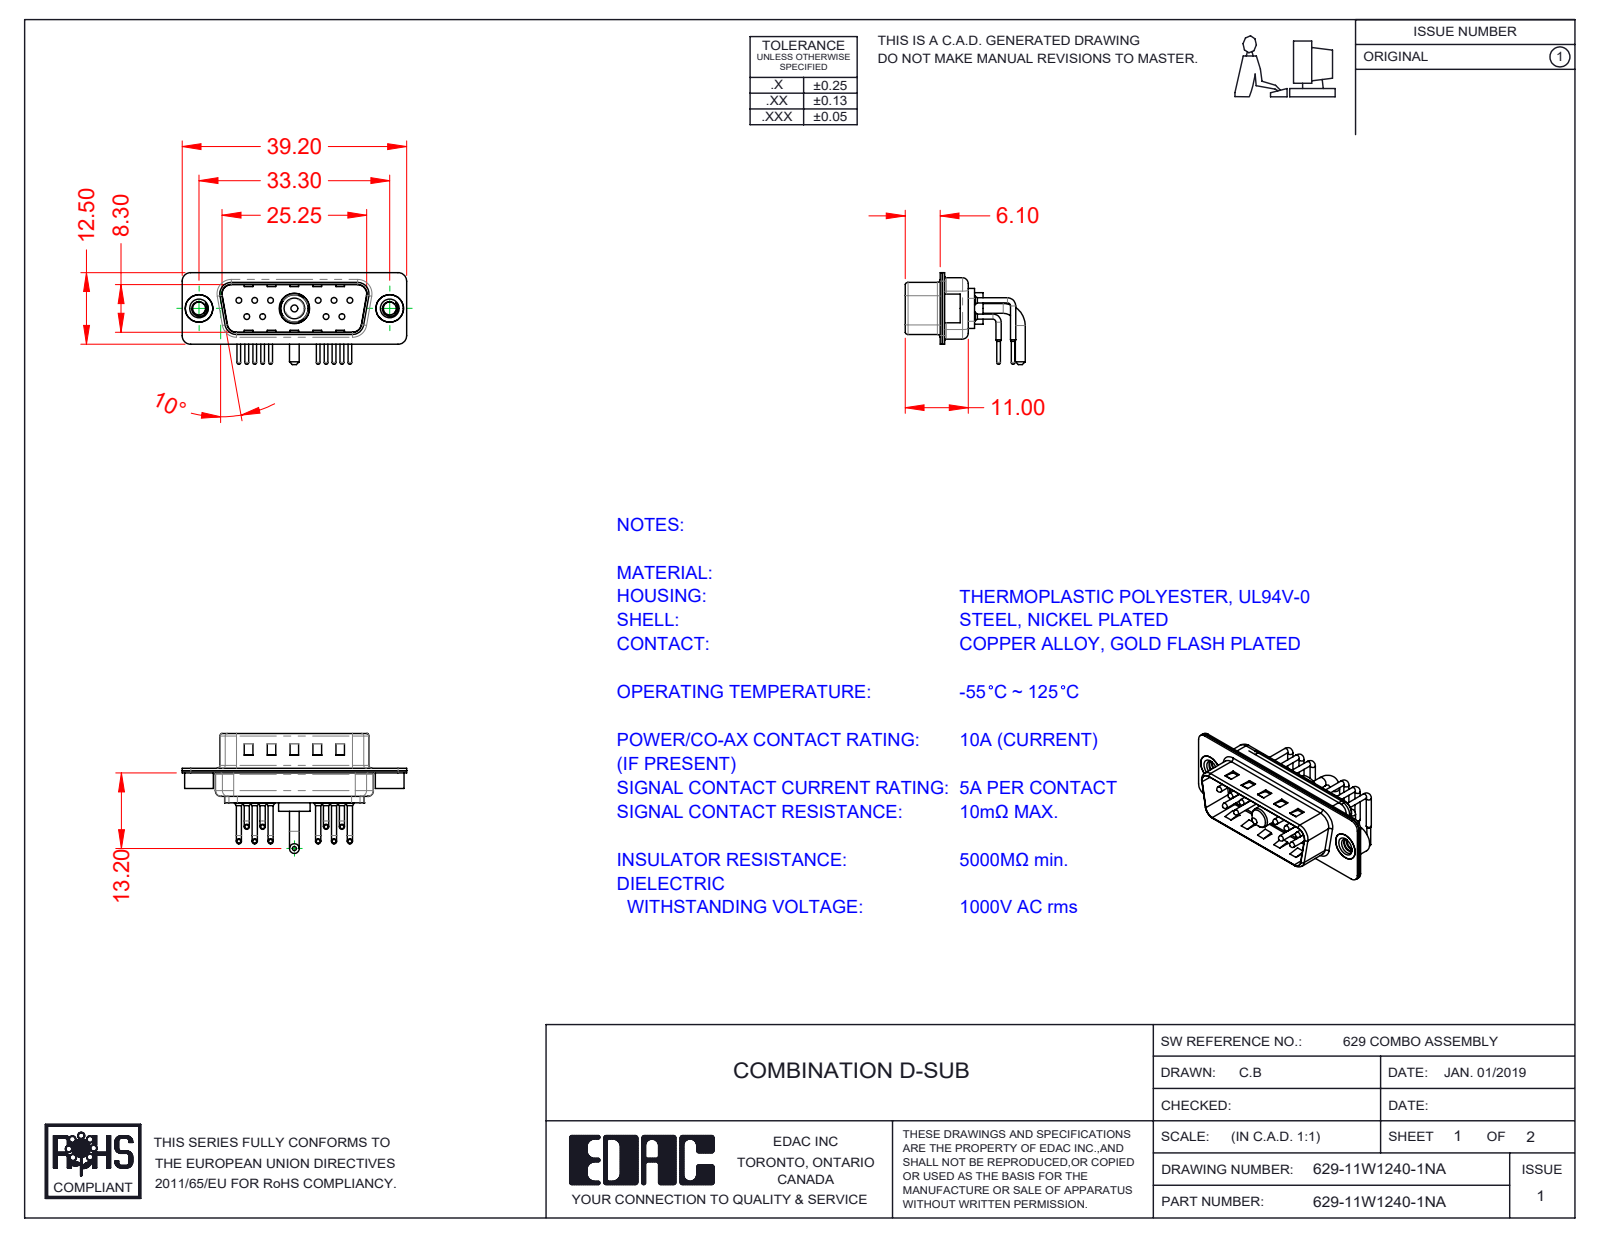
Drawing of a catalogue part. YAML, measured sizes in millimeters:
part_name: "Power Pin_10A RA; 629Combo Threaded Rivet_2; 629Combo Contact Row 1; 629-11W1240-1NA (+4 more)"
step_written_by: "SolidWorks 2020 (CONFIG_CONTROL_DESIGN)"
units: millimeters
bodies: {solids: 17, faces: 1496, planar: 798, cylindrical: 518, other: 180}
overall_size: [39.2, 20.95, 16.05]
volume: 2006
surface_area: 5183
round_holes:
  - {diameter: 0.75, count: 10}
  - {diameter: 1.6, count: 10}
  - {diameter: 2, count: 10}
  - {diameter: 2.26, count: 2}
  - {diameter: 4, count: 2}
  - {diameter: 4.8, count: 2}
  - {diameter: 4.85, count: 1}
  - {diameter: 5.3, count: 1}
round_bosses_or_shafts:
  - {diameter: 0.9, count: 20}
  - {diameter: 1.5, count: 10}
  - {diameter: 1, count: 10}
  - {diameter: 0.65, count: 10}
  - {diameter: 5, count: 2}
  - {diameter: 4.9, count: 2}
  - {diameter: 1.7, count: 2}
  - {diameter: 5.5, count: 1}
partial_cylinders:
  - {radius: 1.5, count: 16}
  - {radius: 2, count: 12}
  - {radius: 1.01, count: 10}
  - {radius: 0.5, count: 8}
  - {radius: 1.6, count: 8}
  - {radius: 1, count: 7}
  - {radius: 0.25, count: 4}
  - {radius: 0.6, count: 4}
face_to_face_distances: [0.4, 0.8, 9.5, 9.1, 8.7, 9.9, 5.6, 0.75, 1.2, 0.35]
hole_center_spacings: [3.16, 2.77, 13.85, 11.08, 16.62, 5.03, 5.04, 5.54]
